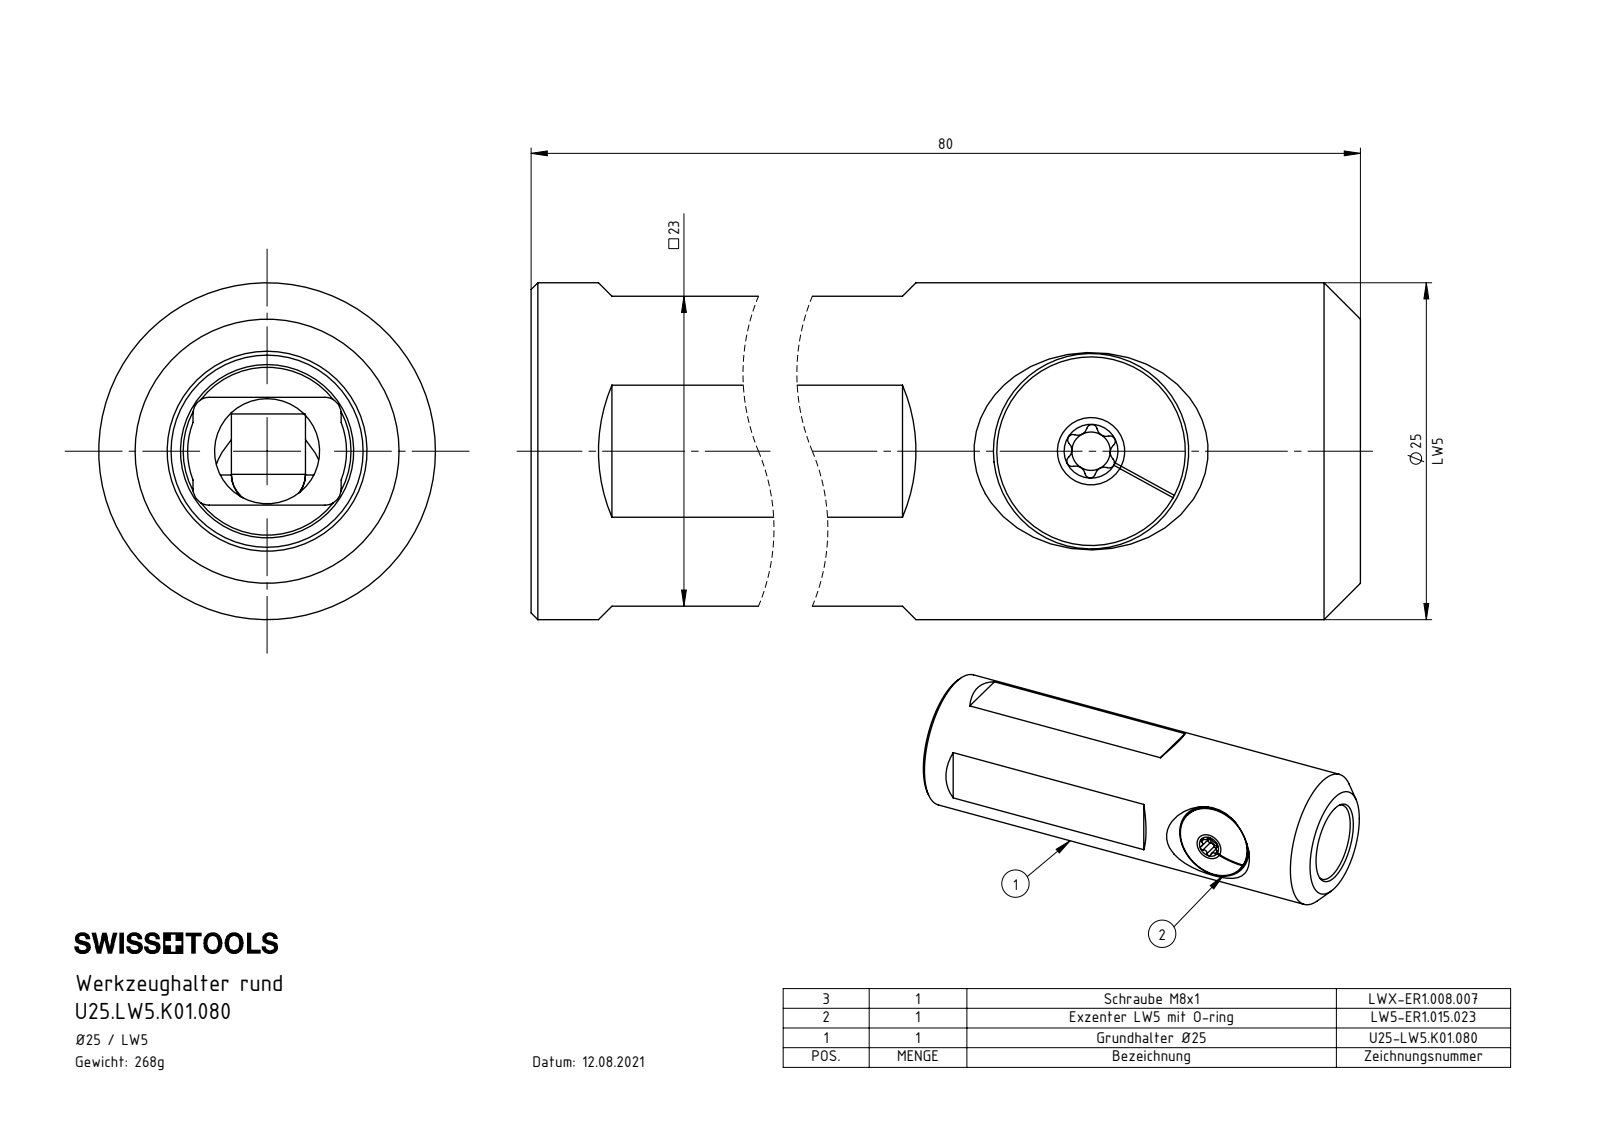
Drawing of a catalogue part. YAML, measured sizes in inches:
part_name: "DIN 3771 - 10x1; LW5-ER1.015.023_A_Standard<Wie bearbeitet>; U25.LW5.K01.080; U25-LW5.K01.080_A (+1 more)"
step_written_by: "SolidWorks 2017 (AUTOMOTIVE_DESIGN)"
units: inches
bodies: {solids: 4, faces: 133, planar: 54, cylindrical: 43, other: 36}
overall_size: [3.15, 0.984, 0.984]
volume: 2.014
surface_area: 16.76
round_holes:
  - {diameter: 0.039, count: 1}
  - {diameter: 0.112, count: 1}
  - {diameter: 0.276, count: 1}
  - {diameter: 0.307, count: 1}
  - {diameter: 0.506, count: 1}
round_bosses_or_shafts:
  - {diameter: 0.984, count: 1}
  - {diameter: 0.551, count: 1}
  - {diameter: 0.472, count: 1}
  - {diameter: 0.402, count: 1}
partial_cylinders:
  - {radius: 0.016, count: 6}
  - {radius: 0.027, count: 6}
  - {radius: 0.047, count: 4}
  - {radius: 0.108, count: 2}
  - {radius: 0.163, count: 2}
  - {radius: 0.161, count: 1}
  - {radius: 0.185, count: 1}
  - {radius: 0.232, count: 1}
face_to_face_distances: [0.906, 0.059, 0.846, 3.15, 0.61, 0.787, 0.295, 0.043, 0.575, 0.618]
